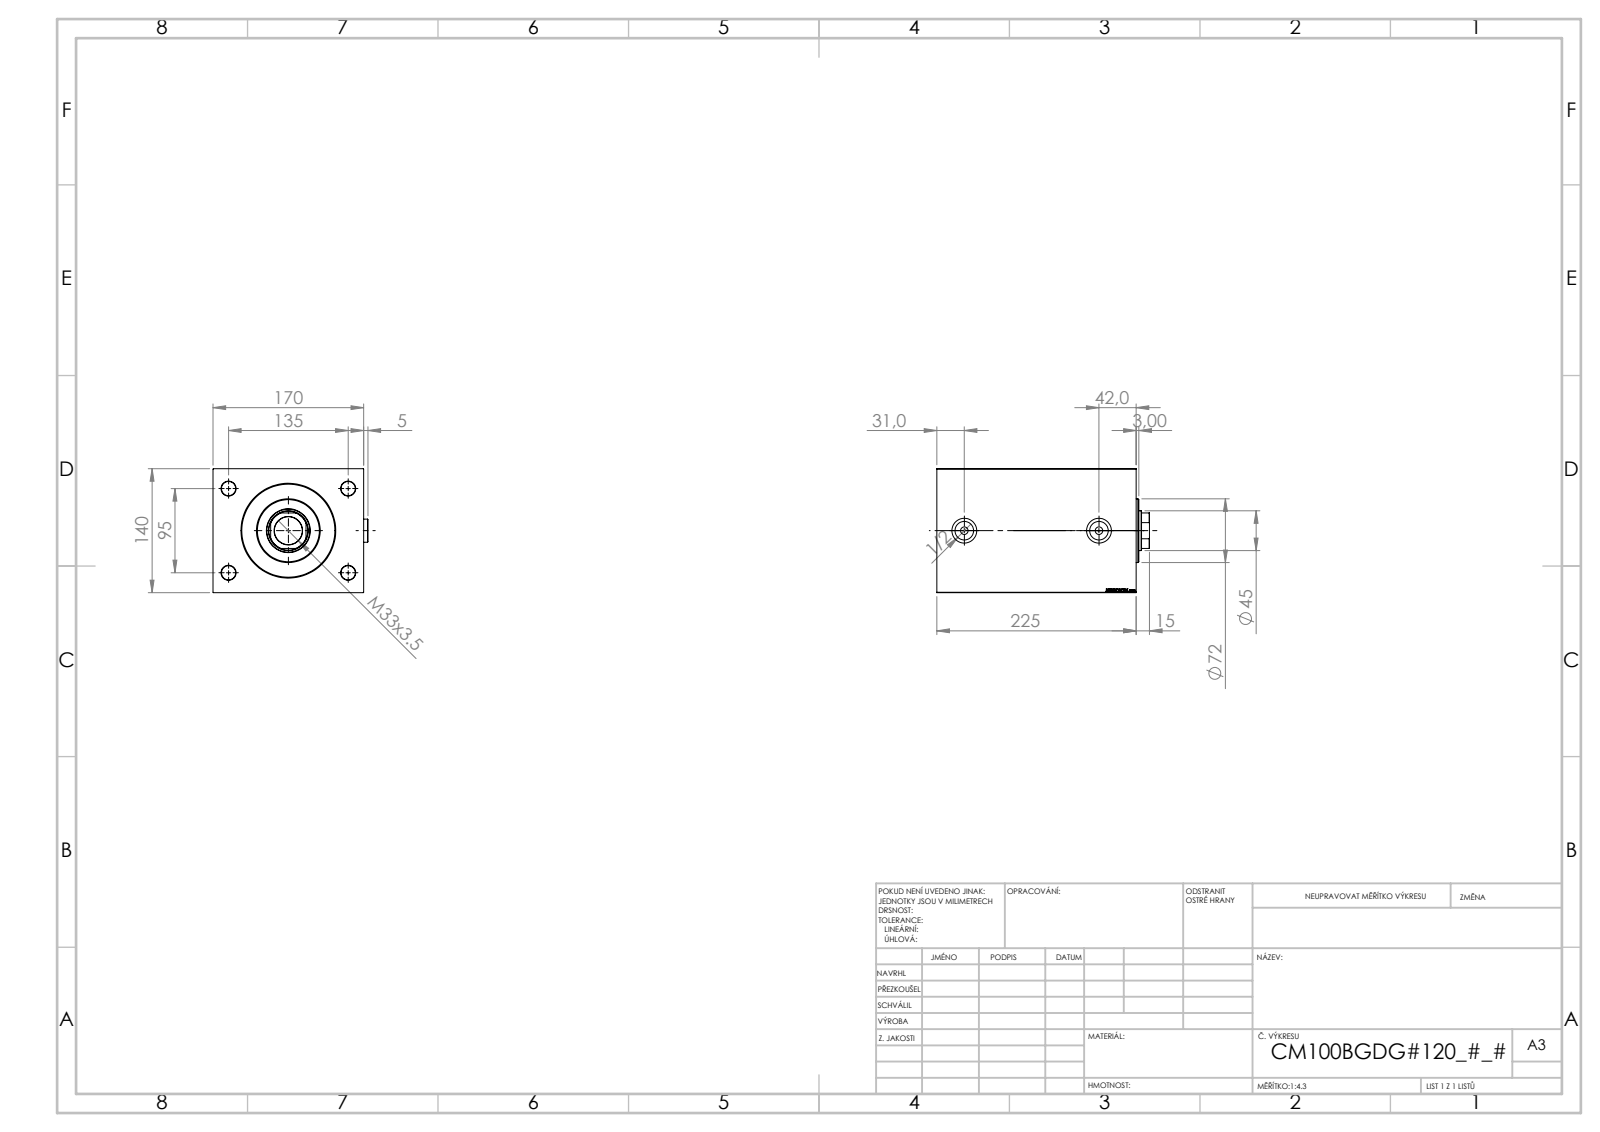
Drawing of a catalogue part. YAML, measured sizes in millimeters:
part_name: "V450CM_B_Body; V450CM_VC_B; Zatka_OIL_PORT; V450CM_B_VCP"
step_written_by: "SolidWorks 2019 (CONFIG_CONTROL_DESIGN)"
units: millimeters
bodies: {solids: 5, faces: 938, planar: 436, cylindrical: 72, other: 430}
overall_size: [240, 174.9, 140]
volume: 4531000
surface_area: 352973
round_holes:
  - {diameter: 16, count: 4}
  - {diameter: 8.5, count: 2}
  - {diameter: 20.96, count: 2}
  - {diameter: 28, count: 2}
  - {diameter: 31.5, count: 1}
  - {diameter: 45, count: 1}
  - {diameter: 48.5, count: 1}
  - {diameter: 49.5, count: 1}
  - {diameter: 100, count: 1}
  - {diameter: 102, count: 1}
  - {diameter: 105, count: 1}
round_bosses_or_shafts:
  - {diameter: 26, count: 2}
  - {diameter: 72, count: 1}
partial_cylinders:
  - {radius: 22, count: 1}
face_to_face_distances: [140, 170, 225, 199, 26, 15, 184, 210, 90, 64]
hole_center_spacings: [82.54, 95, 135, 165.08, 152]
